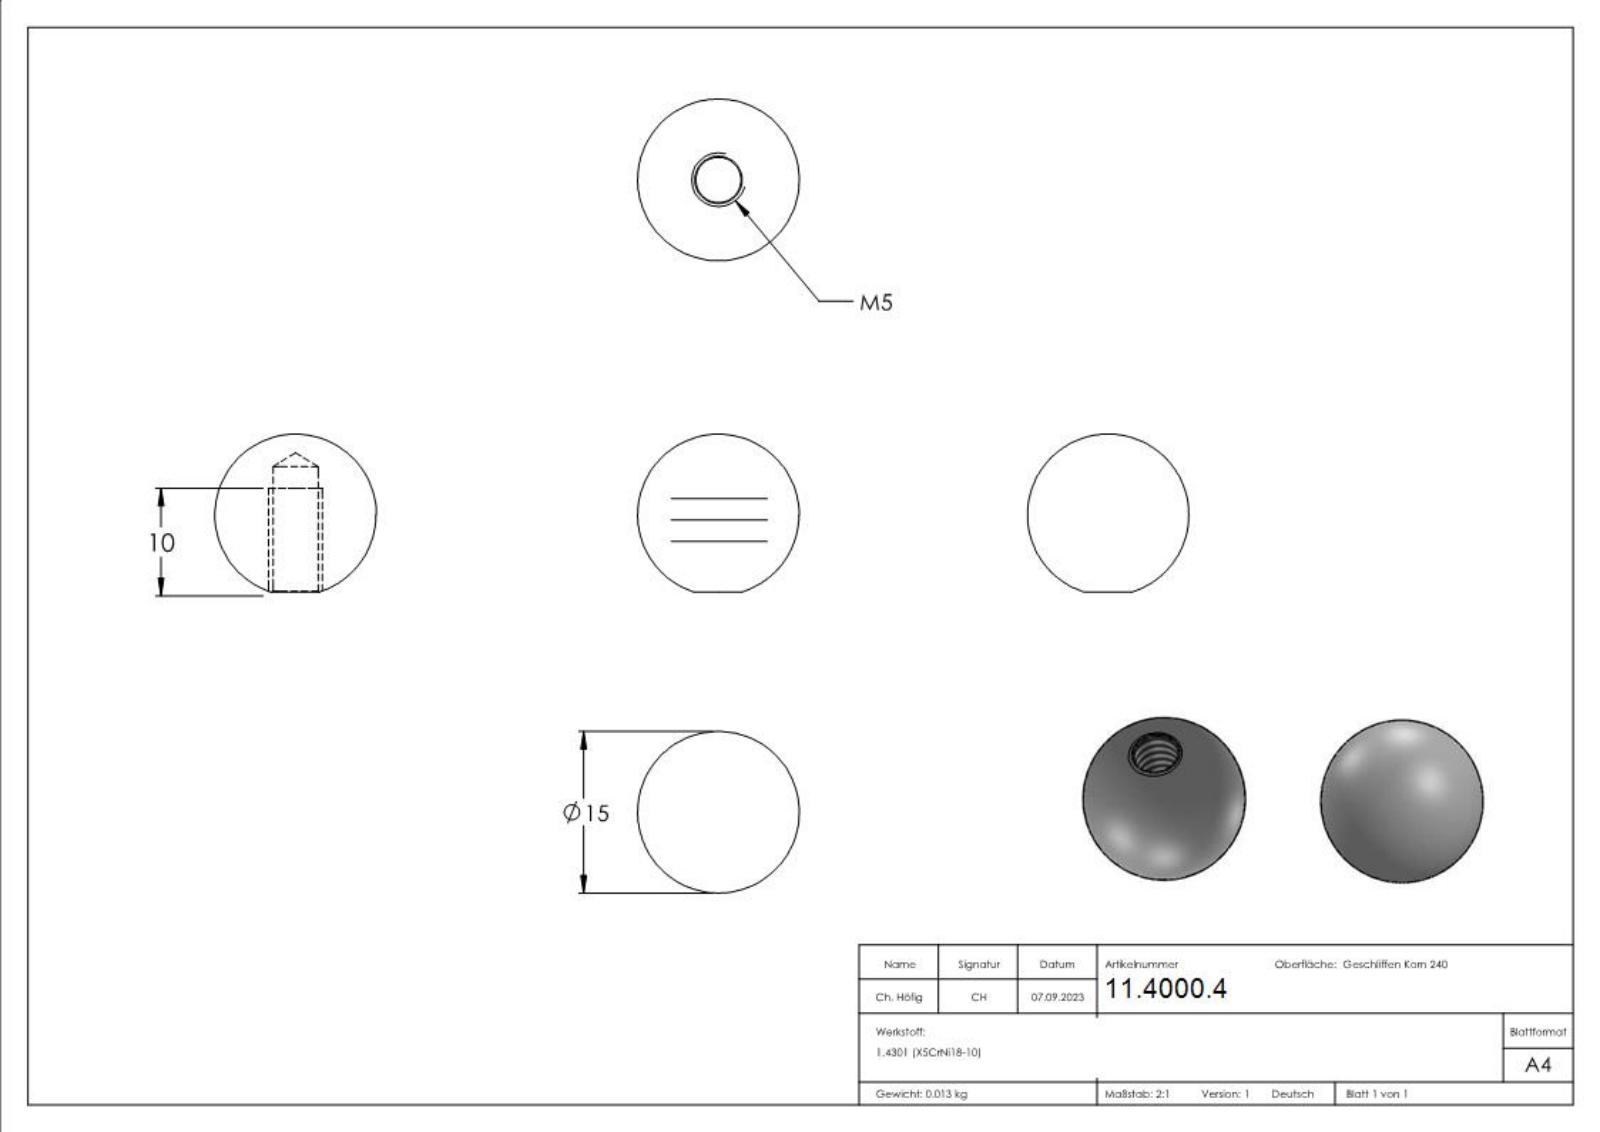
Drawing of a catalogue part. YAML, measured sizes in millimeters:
part_name: "51015-240"
step_written_by: "SolidWorks 2018 (CONFIG_CONTROL_DESIGN)"
units: millimeters
bodies: {solids: 1, faces: 4, planar: 0, cylindrical: 1, other: 3}
overall_size: [15, 15, 14.67]
volume: 1597
surface_area: 862
round_holes:
  - {diameter: 4.2, count: 1}
